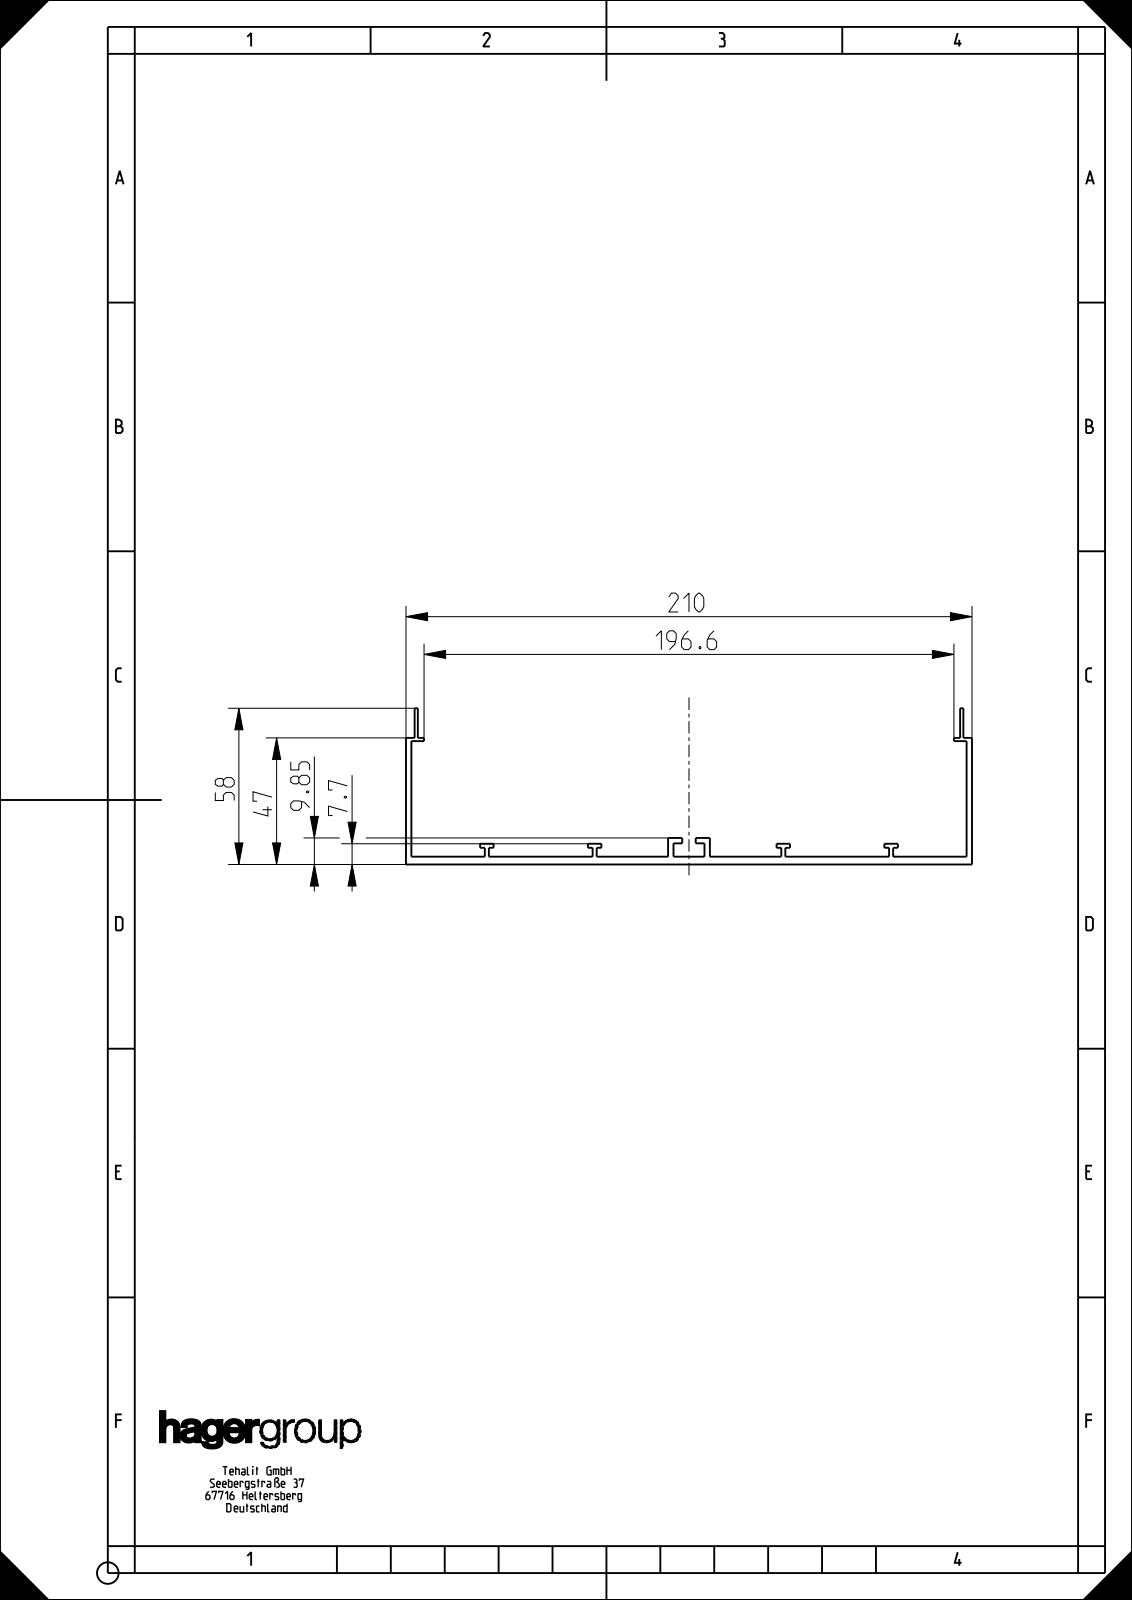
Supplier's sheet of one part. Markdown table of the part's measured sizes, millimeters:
| quantity | value |
| --- | --- |
| part name | BRN652101KUN |
| STEP written by | CREO PARAMETRIC BY PTC INC, 2022162 (AUTOMOTIVE_DESIGN) |
| units | millimeters |
| bodies | 1 solid, 1986 faces (1826 planar, 160 cylindrical, 0 other) |
| overall size | 2000 × 210 × 58 |
| volume | 1 807 000 mm³ |
| surface area | 1 548 000 mm² |
| partial cylindrical surfaces (radius × count) | 2.3 × 80, 3.25 × 40 |
| main face-to-face distances | 2.9, 2, 208, 1.2, 210, 206, 203.6, 1.5, 97.25, 110.75 |
